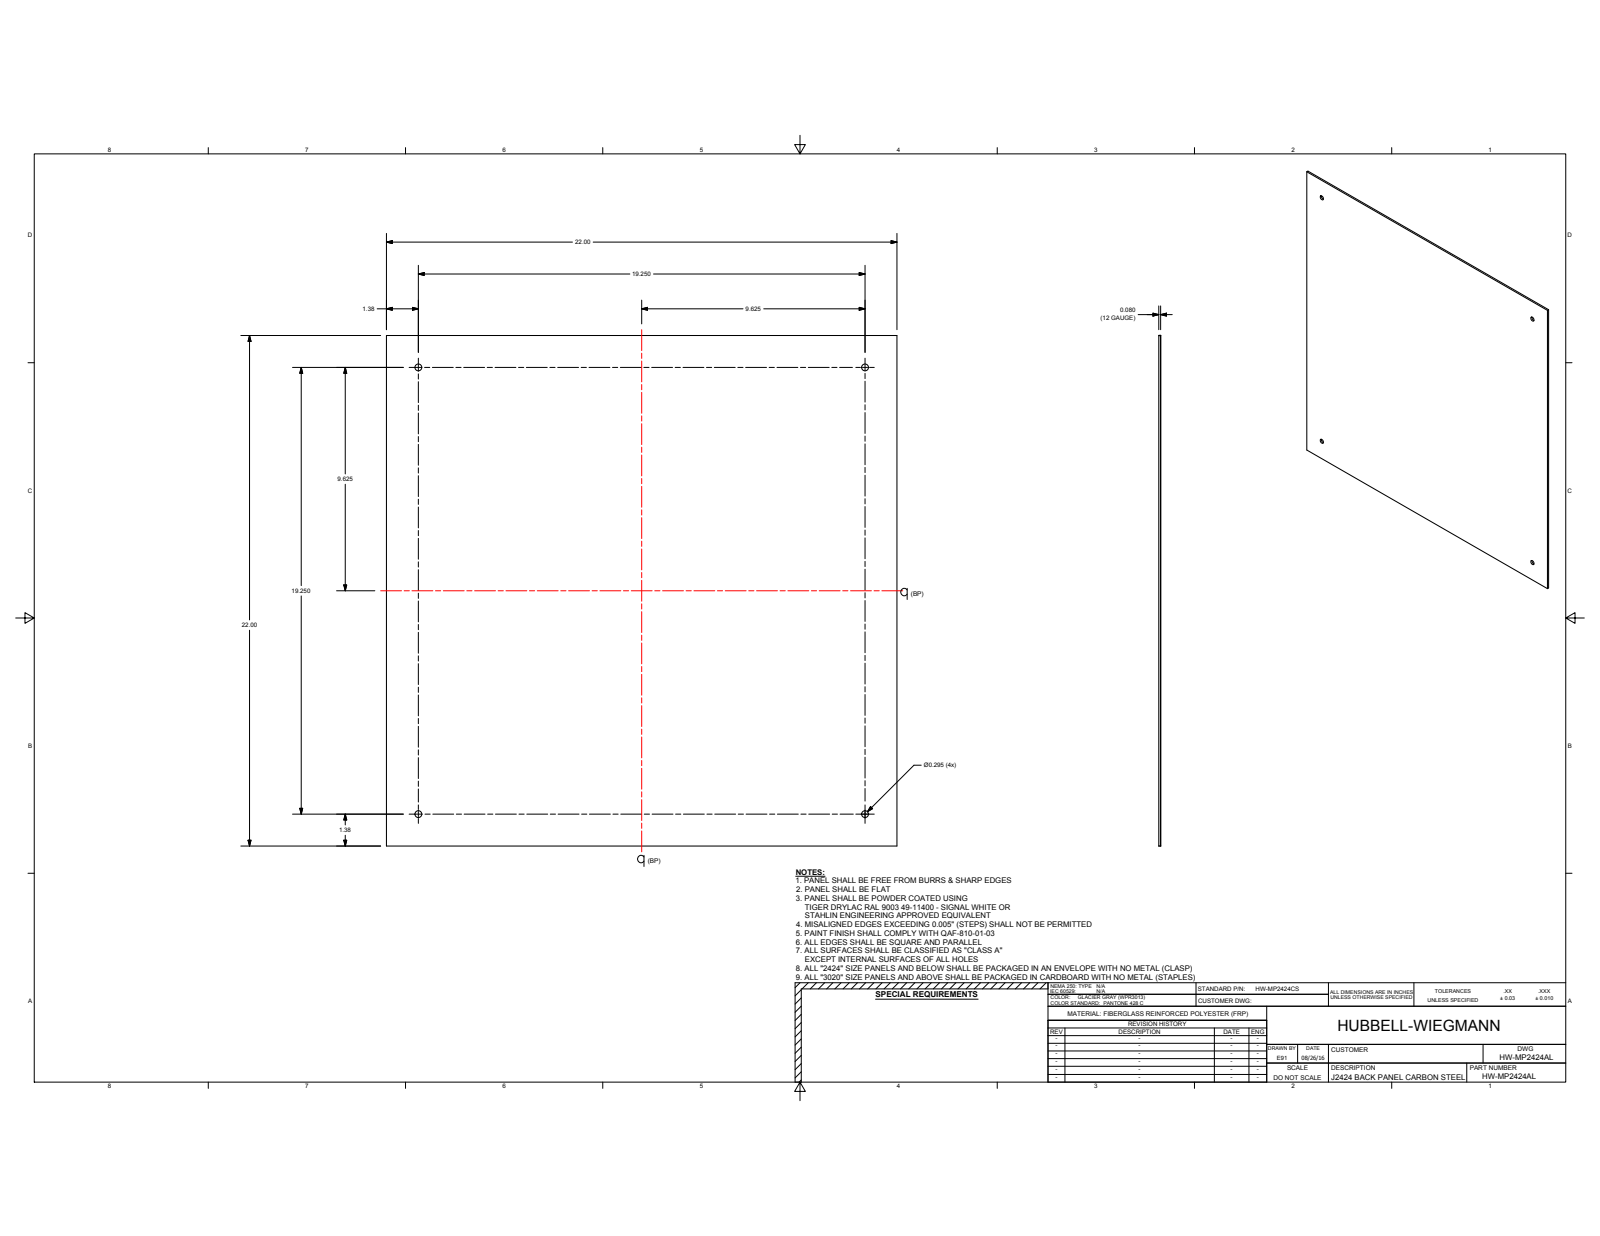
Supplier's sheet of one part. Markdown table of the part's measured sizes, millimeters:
| quantity | value |
| --- | --- |
| part name | HW-MP2424AL |
| STEP written by | Autodesk Inventor 2017 (CONFIG_CONTROL_DESIGN) |
| units | millimeters |
| bodies | 1 solid, 10 faces (6 planar, 4 cylindrical, 0 other) |
| overall size | 558.8 × 558.8 × 2.03 |
| volume | 634 149 mm³ |
| surface area | 628 895 mm² |
| round holes (diameter × count) | 7.49 × 4 |
| main face-to-face distances | 2.03, 558.8 |
| hole center spacings | 488.96, 691.49 |
